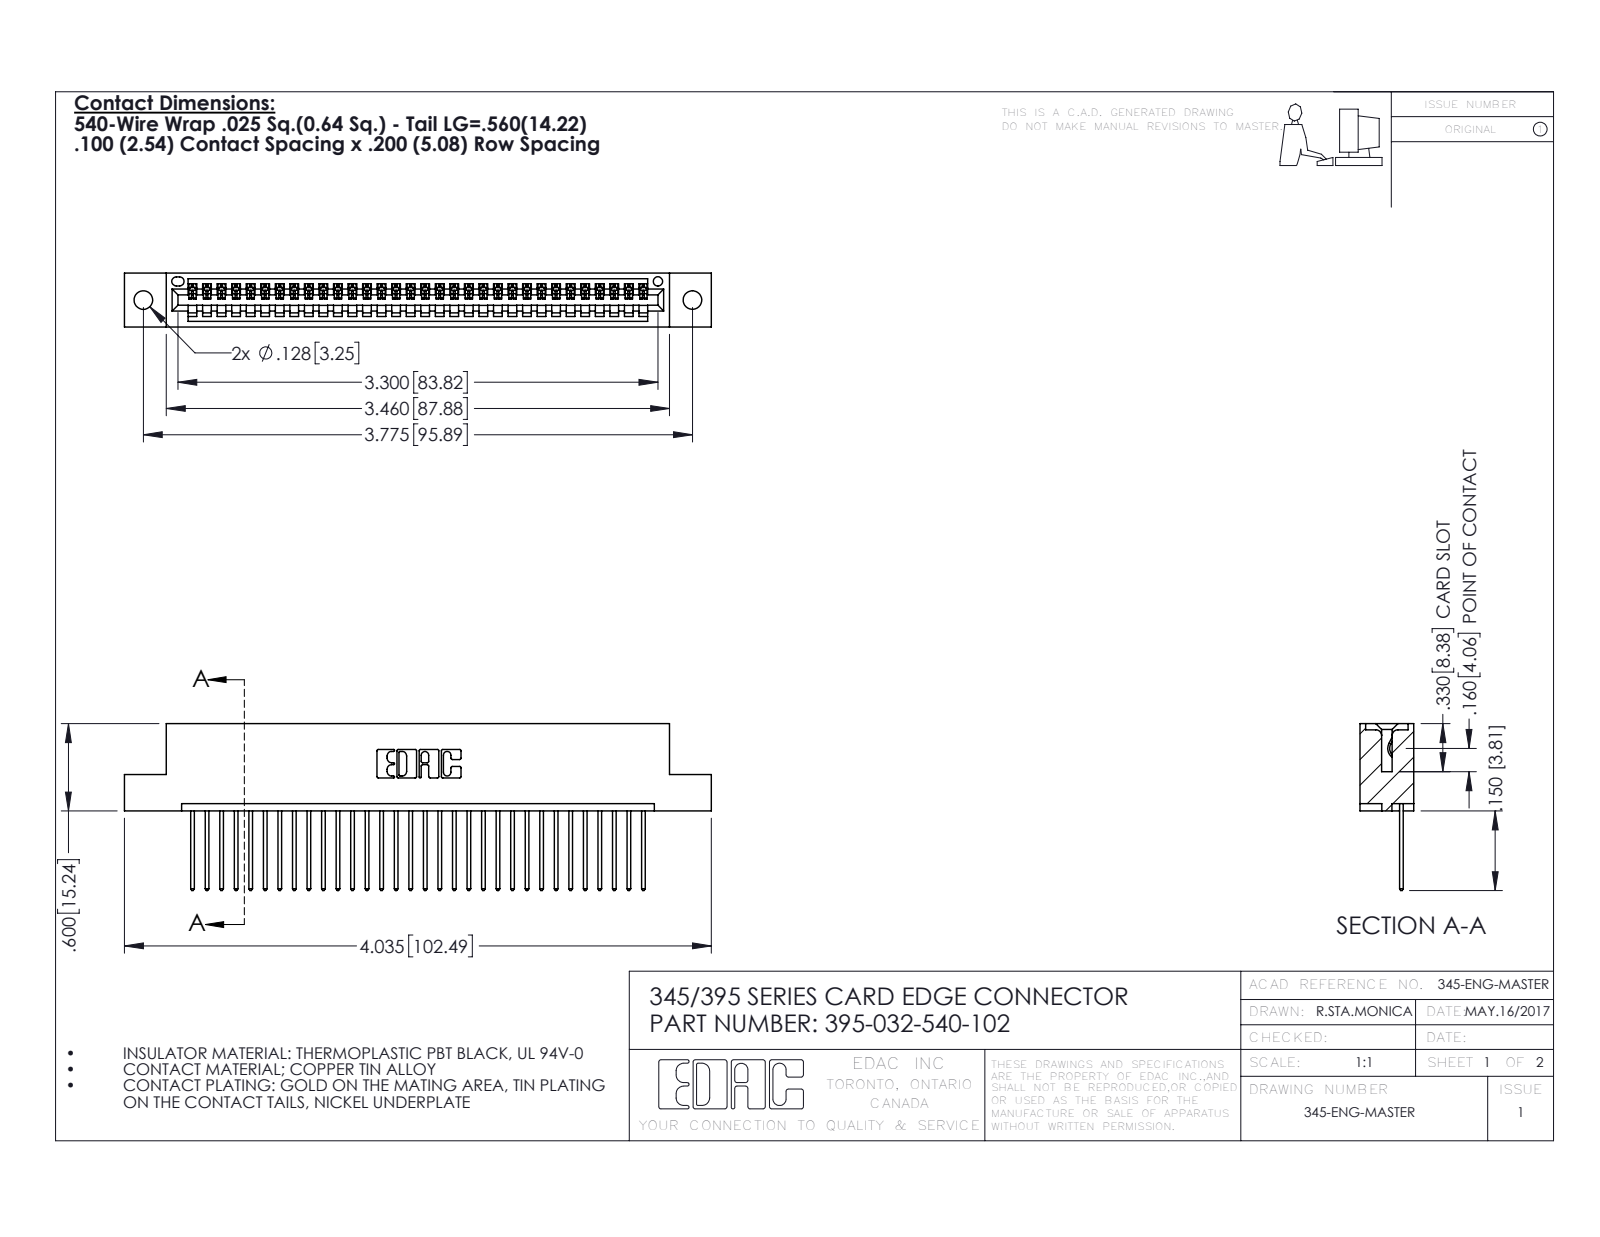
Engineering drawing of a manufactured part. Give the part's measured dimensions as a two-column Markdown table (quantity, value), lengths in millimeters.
| quantity | value |
| --- | --- |
| part name | 395-032-540-102; 345 Part_Flush Mounting Lugs - 0.128 Dia; 345-292-001_345-293-140 |
| STEP written by | SolidWorks 2016 (CONFIG_CONTROL_DESIGN) |
| units | millimeters |
| bodies | 33 solids, 1982 faces (1360 planar, 622 cylindrical, 0 other) |
| overall size | 102.5 × 29.1 × 9.4 |
| volume | 9 650 mm³ |
| surface area | 12 740 mm² |
| round holes (diameter × count) | 3.3 × 2, 1.6 × 1 |
| partial cylindrical surfaces (radius × count) | 0.2 × 64, 0.3 × 64, 0.3 × 22, 0.2 × 6, 0.8 × 6, 0.7 × 3, 0.8 × 2, 1 × 2 |
| main face-to-face distances | 7.6, 1.8, 5.1, 9.4, 2.5, 6.9, 0.6, 5.7, 3.8, 1.8 |
| hole center spacings | 6.9, 89.9, 95.9 |
